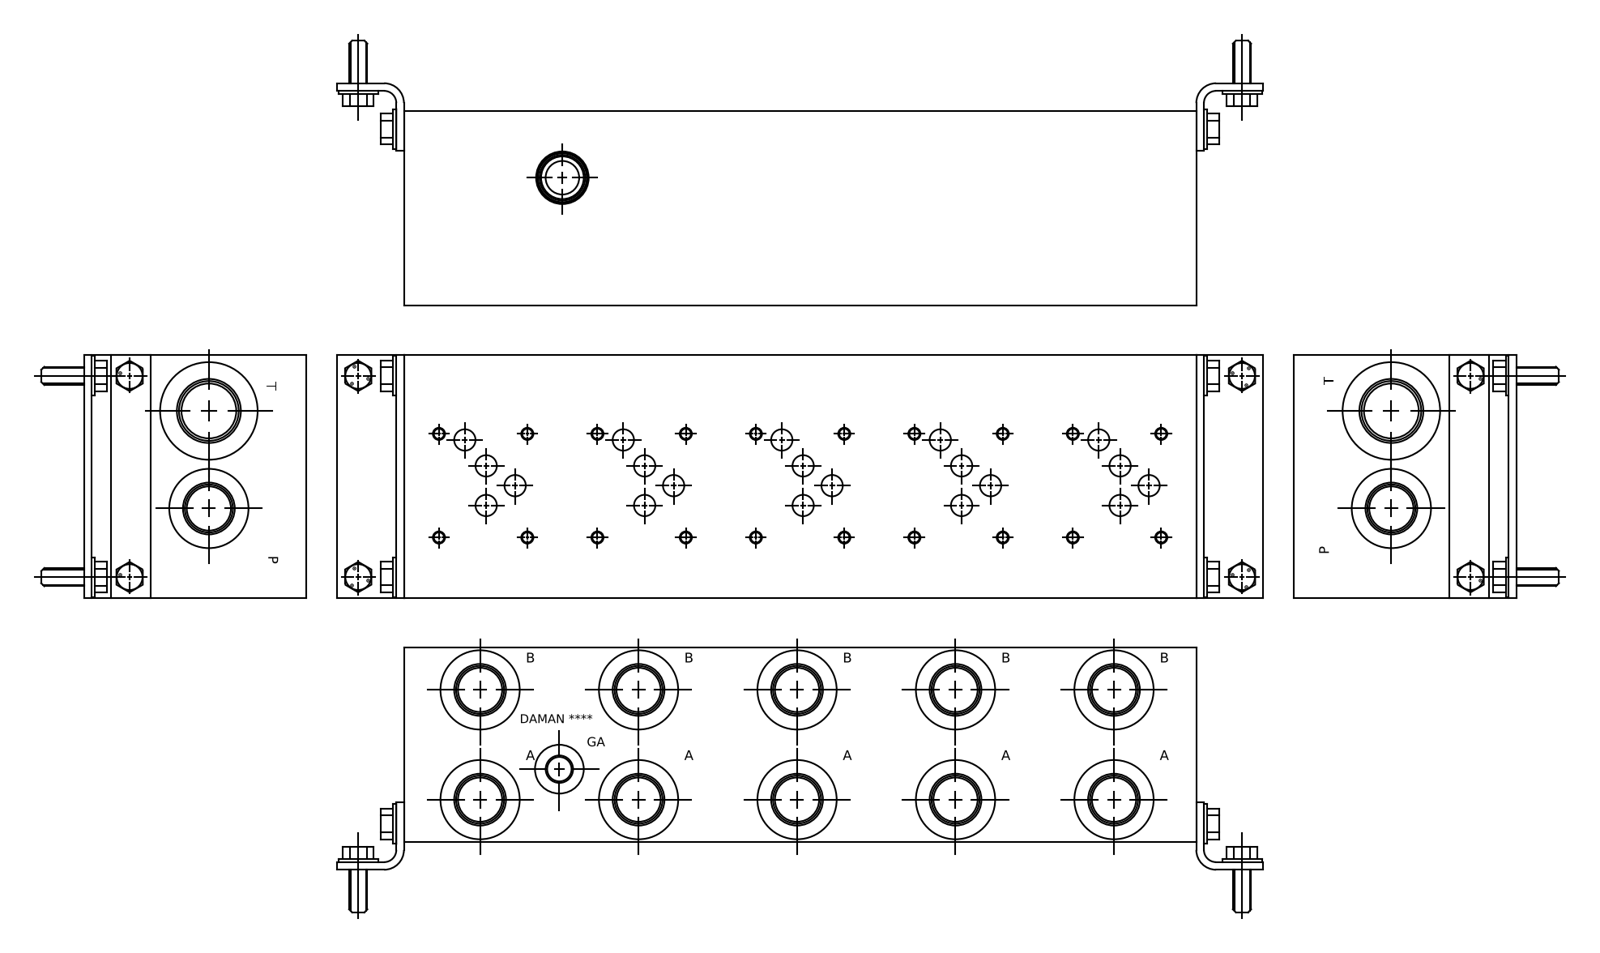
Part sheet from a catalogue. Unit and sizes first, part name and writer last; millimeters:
Units: millimetres
Overall size (bounding box): 412.75 × 127 × 101.6
Round holes (diameter × count): ⌀5.11 ×20, ⌀6.35 ×20, ⌀11.13 ×18, ⌀23.01 ×11, ⌀24.92 ×11, ⌀27.43 ×11, ⌀42.04 ×11, ⌀27 ×10, ⌀7.92 ×2, ⌀9.53 ×2, ⌀11.11 ×2, ⌀26.99 ×2
Main face-to-face distances: 101.6, 127, 0.79, 412.75, 126.21, 411.96, 411.17, 19.05, 19.84, 107.16
Hole centre spacings: 82.55, 165.1, 247.65, 18.27, 68.25, 100.4, 85.09, 98.17
Volume: 4 988 000 mm³ · Surface area: 272 836 mm²
Bodies: 1 solid, 967 faces (482 planar, 151 cylindrical, 334 other)
Part name (STEP PRODUCT): Part_AD05HP053S~S_3D
STEP written by: Autodesk Inventor 2019 (AUTOMOTIVE_DESIGN)
